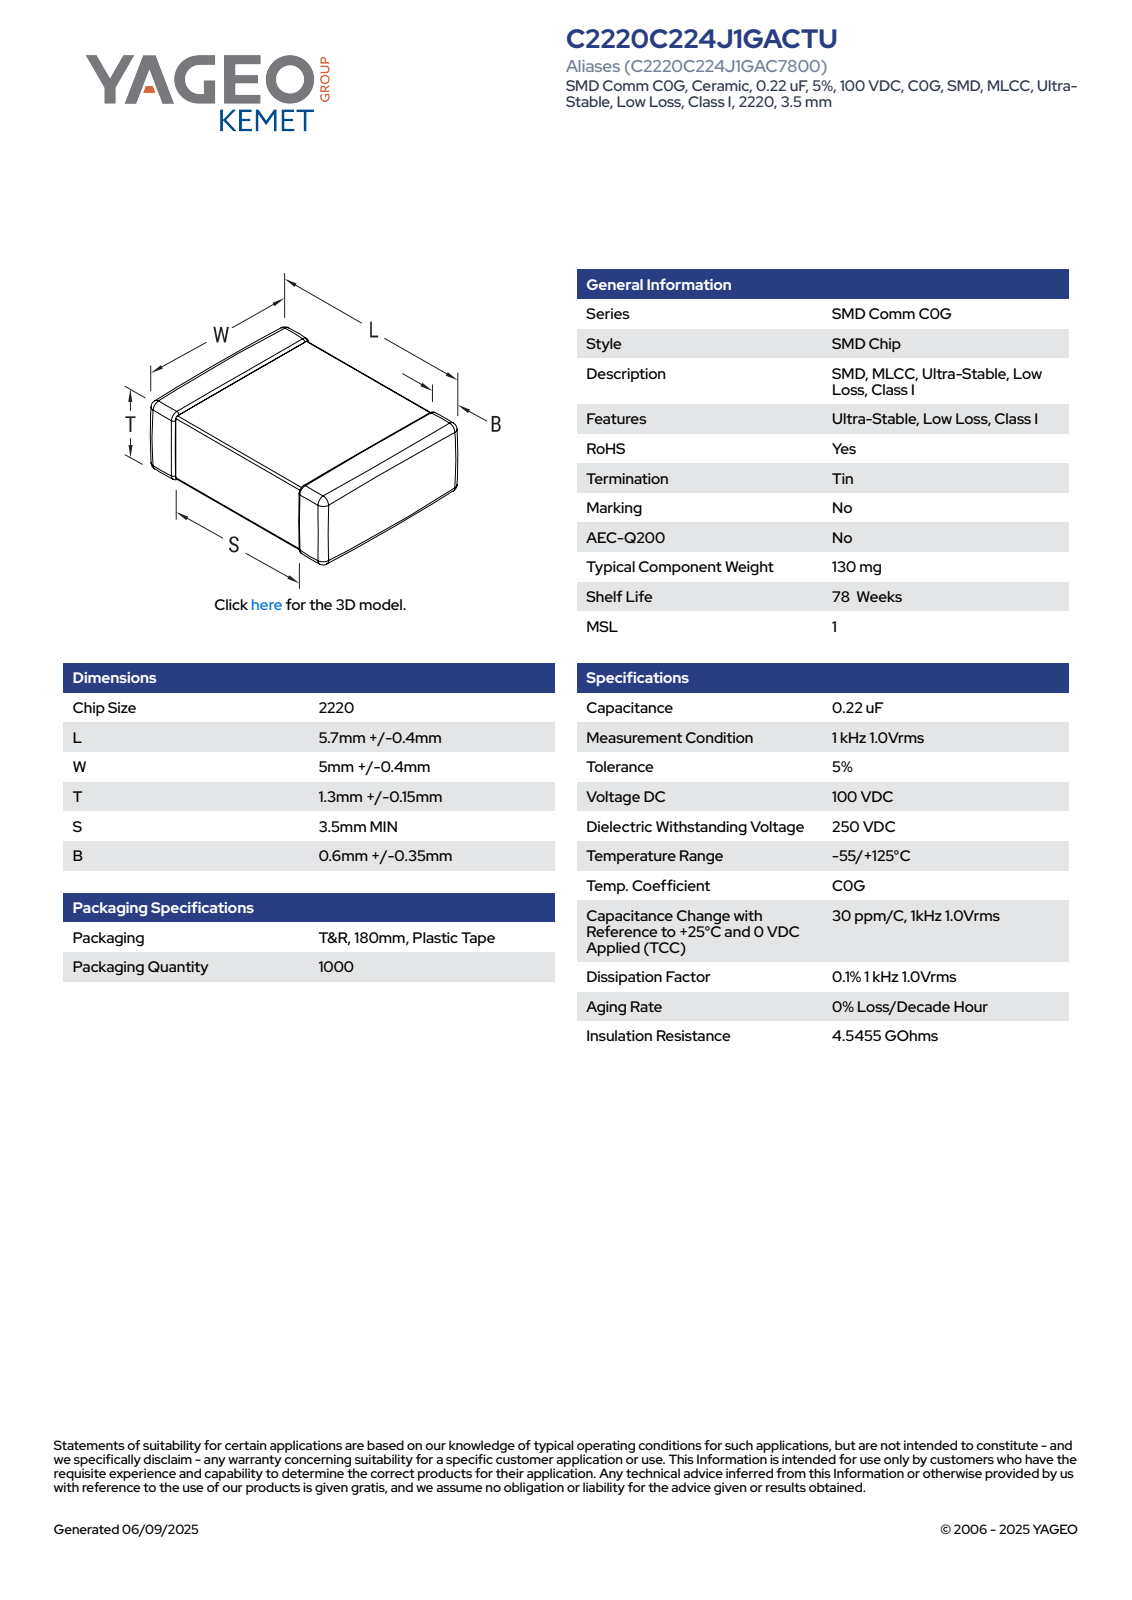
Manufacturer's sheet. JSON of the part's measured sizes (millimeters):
{"part_name": "CCS_CCSTDNOS_2220_L6.1W5.4T1.45B0.95", "step_written_by": "SolidWorks 2014 (AUTOMOTIVE_DESIGN)", "units": "millimeters", "bodies": {"solids": 4, "faces": 125, "planar": 71, "cylindrical": 38, "other": 16}, "overall_size": [6.1, 5.4, 1.45], "volume_mm3": 41, "surface_area_mm2": 96, "partial_cylinders_radius": [[0.11, 24]], "face_to_face_distances": [1.23, 1.34, 1.45, 6.1, 5.18, 5.29, 5.4, 2.66, 2.74, 2.55]}
